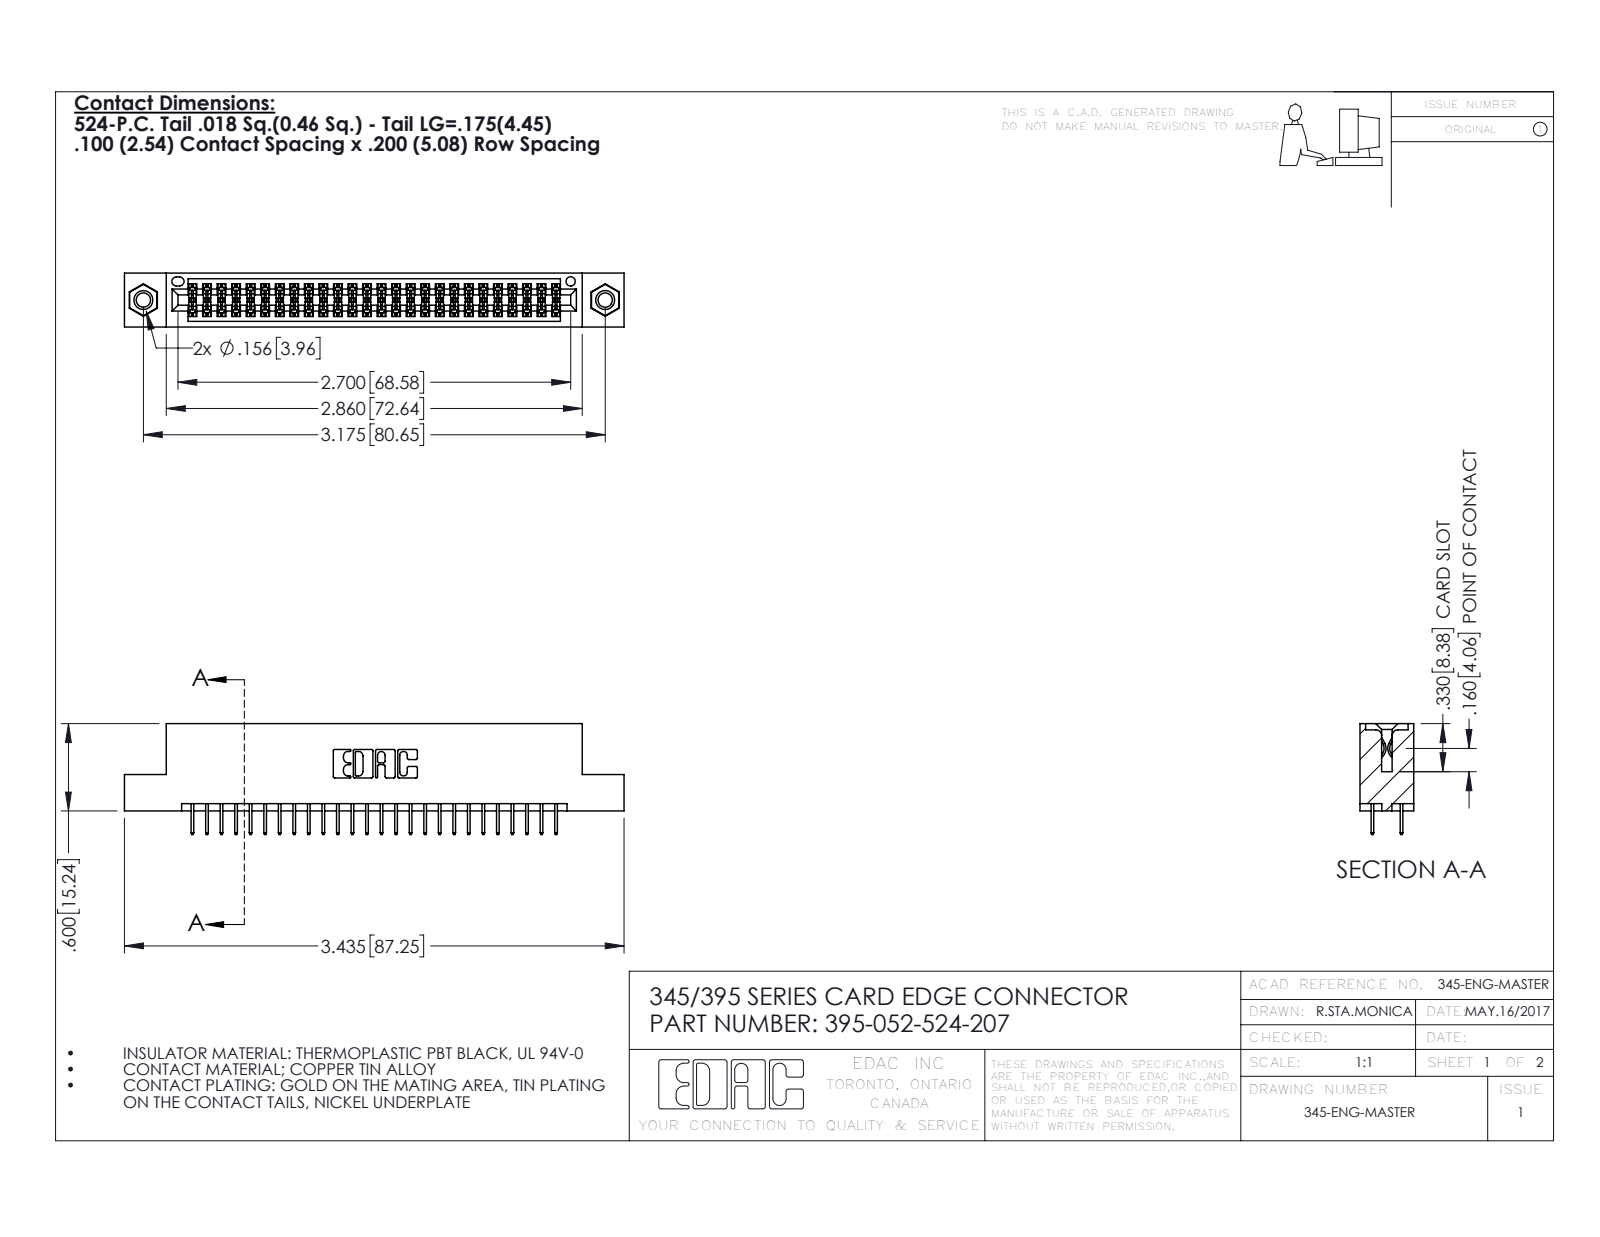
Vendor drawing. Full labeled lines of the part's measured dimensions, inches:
Part name (STEP PRODUCT): 395-052-524-207; 345-250-001_345-250-005-103; 345 Part_Flush Mounting Lugs - 0.156 Dia-TI; 345-292-001_345-293-124
STEP written by: SolidWorks 2016 (CONFIG_CONTROL_DESIGN)
Units: inches
Bodies: 55 solids, 2994 faces (2140 planar, 838 cylindrical, 16 other)
Overall size (bounding box): 3.435 × 0.762 × 0.37
Volume: 0.503 in³ · Surface area: 18.11 in²
Round holes (diameter × count): ⌀0.098 ×2, ⌀0.125 ×2, ⌀0.156 ×2, ⌀0.064 ×1
Round bosses / shafts (diameter × count): ⌀0.155 ×2
Partial cylindrical surfaces — rounded edges, fillets, slot ends (radius × count): R0.006 ×78, R0.01 ×22, R0.007 ×6, R0.031 ×6, R0.026 ×3, R0.014 ×2, R0.019 ×2, R0.022 ×2
Main face-to-face distances: 0.072, 0.298, 0.2, 0.37, 0.098, 0.272, 0.025, 0.225, 0.072, 0.175
Hole centre spacings: 0.27, 2.94, 3.175
